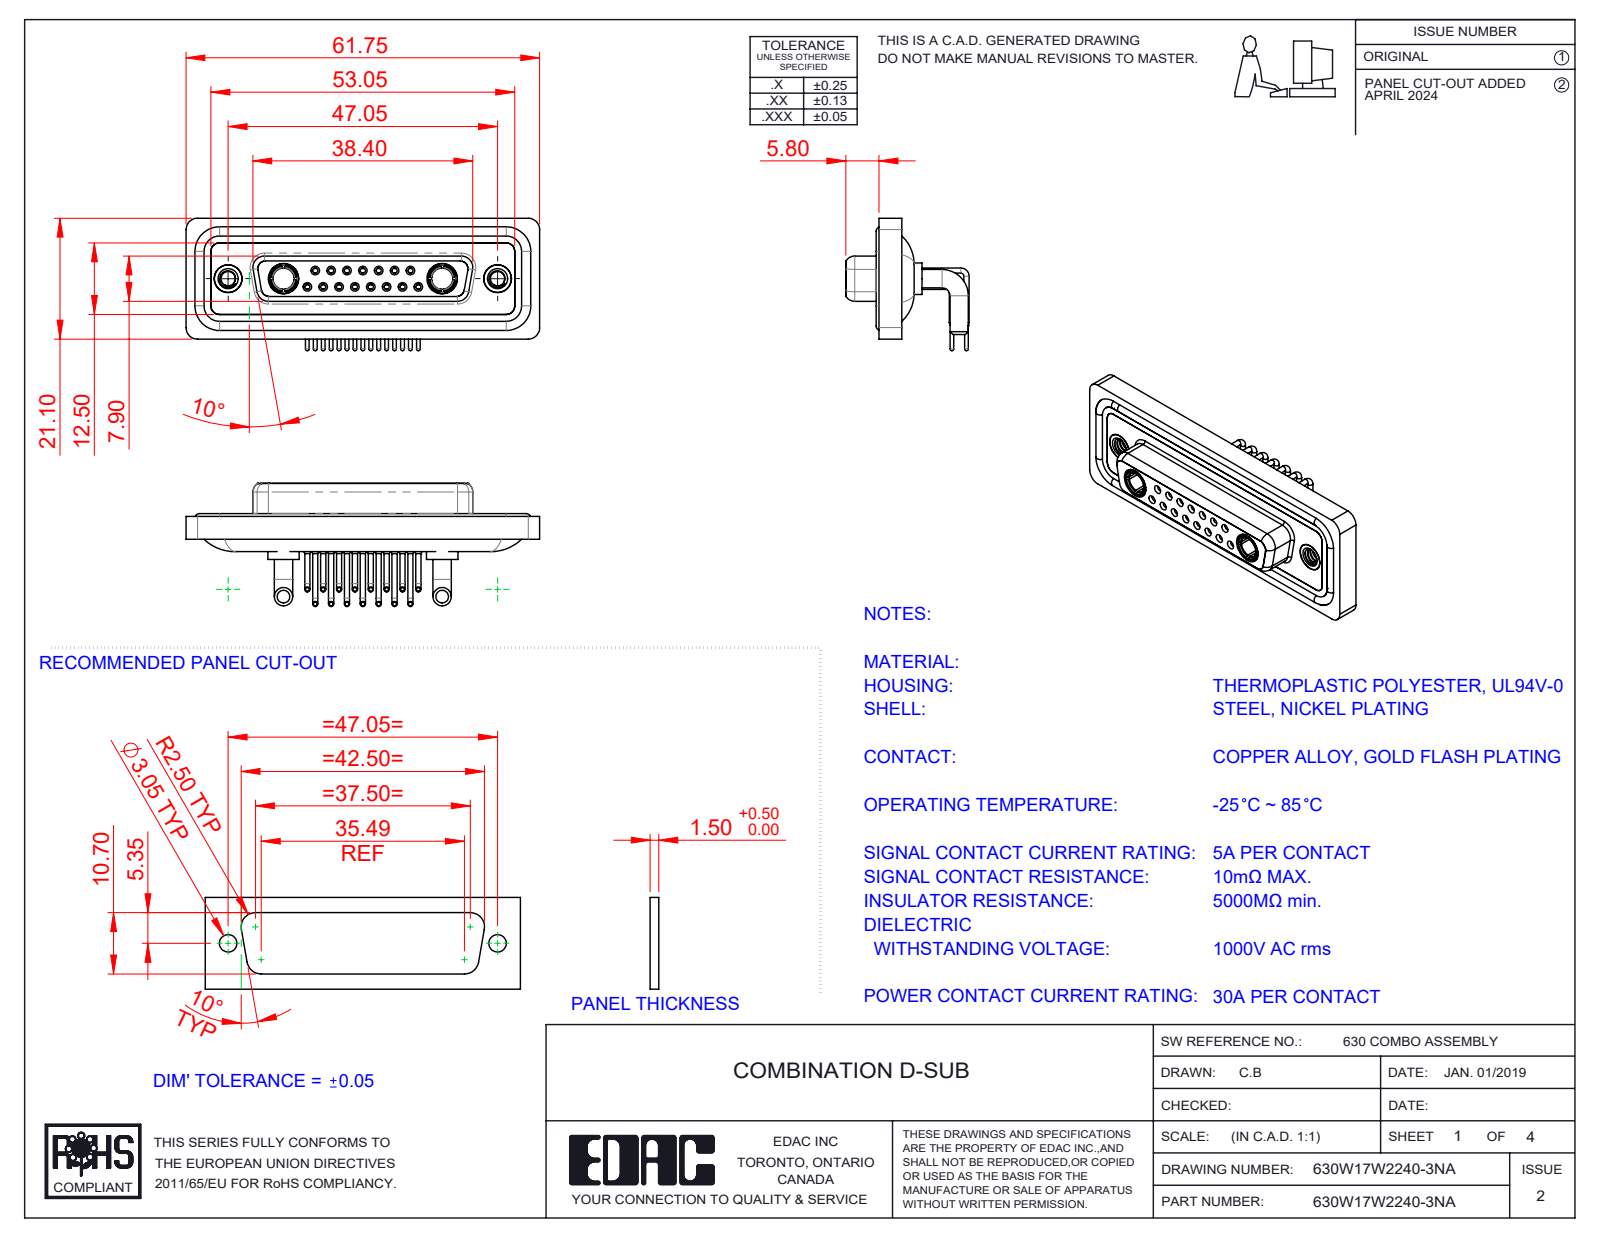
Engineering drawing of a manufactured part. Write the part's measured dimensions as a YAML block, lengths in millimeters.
part_name: "630Combo Contact Row 2_50 Contacts; 630Combo Shell Front_25 Contacts; 630Combo Shell Rear_25 Contacts; 630W17W2140-3NA (+5 more)"
step_written_by: "SolidWorks 2023 (CONFIG_CONTROL_DESIGN)"
units: millimeters
bodies: {solids: 26, faces: 1331, planar: 388, cylindrical: 581, other: 362}
overall_size: [61.75, 23.12, 21.53]
volume: 8535
surface_area: 14570
round_holes:
  - {diameter: 0.9, count: 15}
  - {diameter: 1.1, count: 15}
  - {diameter: 1.5, count: 15}
  - {diameter: 2, count: 15}
  - {diameter: 1.6, count: 8}
  - {diameter: 1.7, count: 7}
  - {diameter: 4.85, count: 4}
  - {diameter: 2.5, count: 2}
  - {diameter: 3.7, count: 2}
  - {diameter: 4, count: 2}
  - {diameter: 4.05, count: 2}
  - {diameter: 5, count: 2}
round_bosses_or_shafts:
  - {diameter: 0.9, count: 15}
  - {diameter: 0.65, count: 15}
  - {diameter: 1.6, count: 11}
  - {diameter: 3.2, count: 4}
  - {diameter: 5.5, count: 2}
  - {diameter: 5.2, count: 2}
  - {diameter: 4.96, count: 2}
  - {diameter: 4.95, count: 2}
partial_cylinders:
  - {radius: 1.5, count: 18}
  - {radius: 2, count: 18}
  - {radius: 1.35, count: 8}
  - {radius: 1.6, count: 8}
  - {radius: 0.25, count: 4}
  - {radius: 0.5, count: 4}
  - {radius: 0.6, count: 4}
  - {radius: 0.65, count: 4}
face_to_face_distances: [0.4, 1.8, 4.1, 1.1, 1.6, 3.1, 2.5, 1.5, 3.7, 1.4]
hole_center_spacings: [3.16, 2.77, 5.54, 8.31, 5.04, 7.49, 11.08, 5.03]
